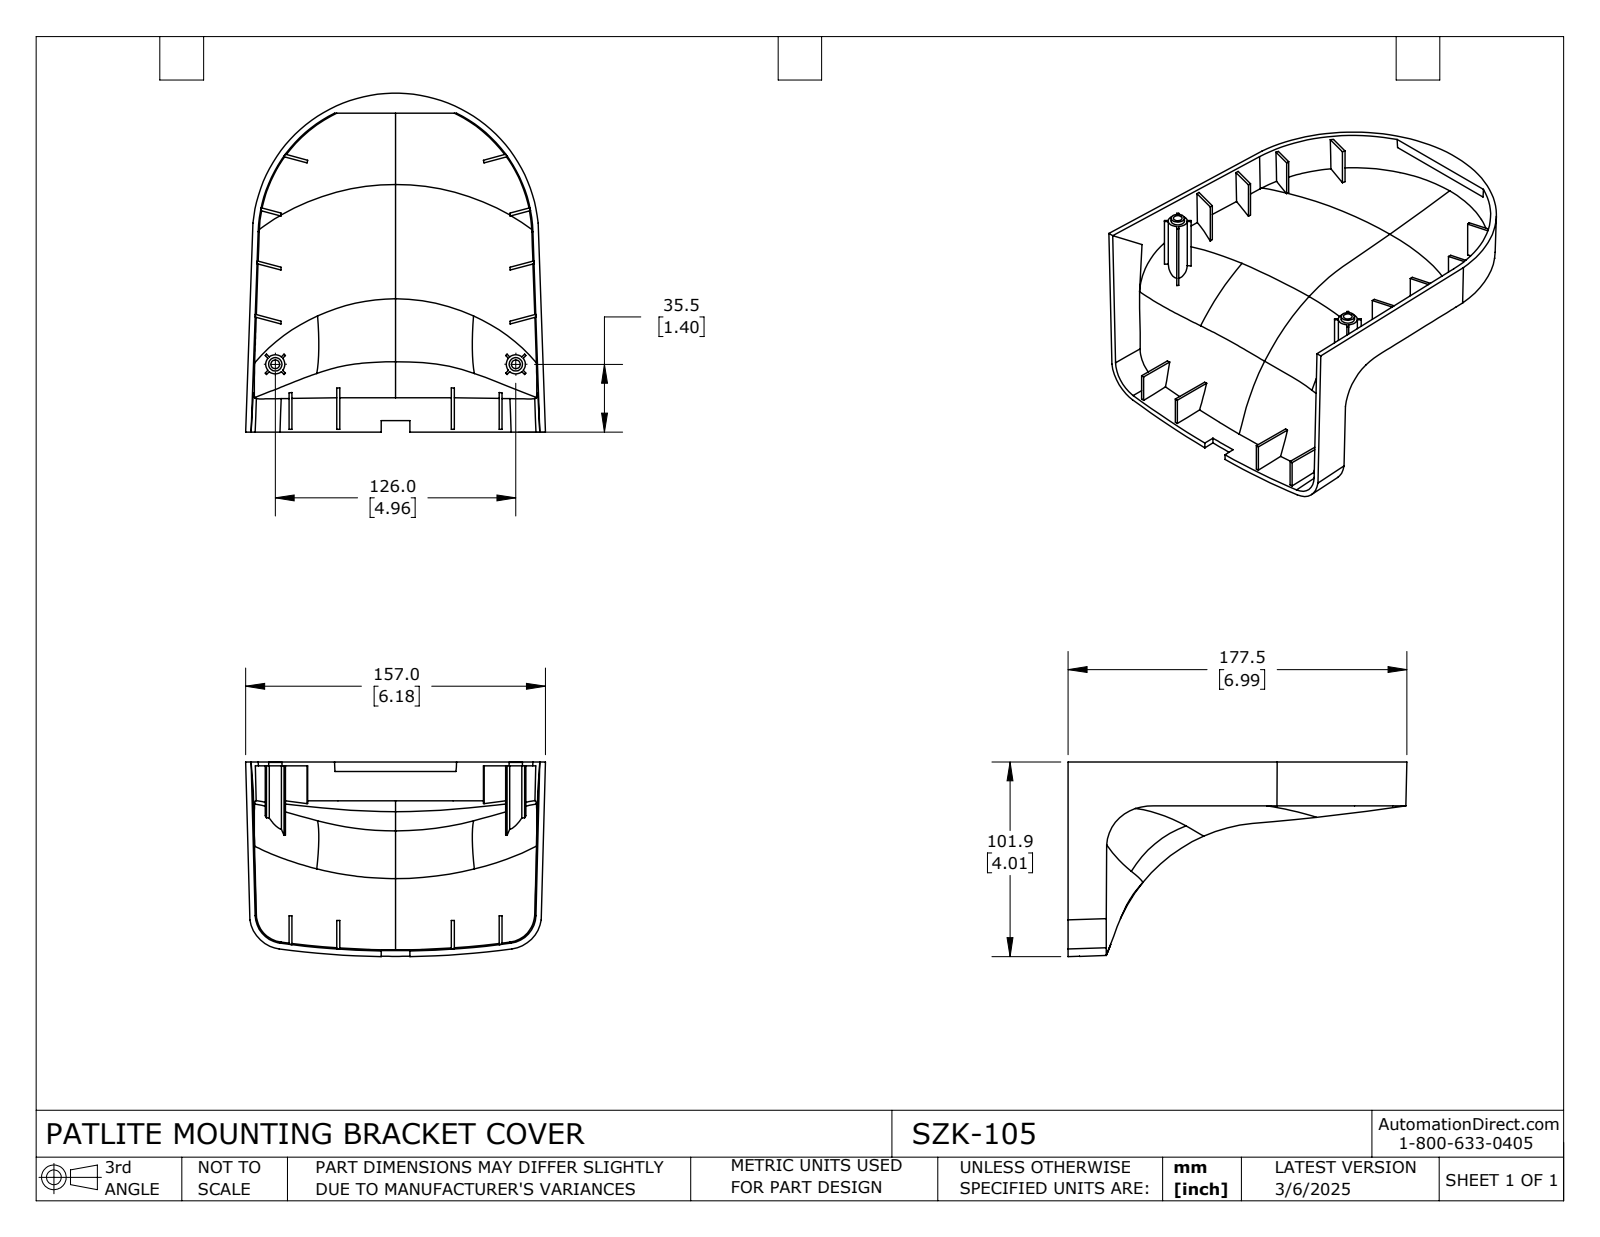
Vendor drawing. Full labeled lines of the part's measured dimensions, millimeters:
Part name (STEP PRODUCT): SZK-105
STEP written by: SolidWorks 2024 (CONFIG_CONTROL_DESIGN)
Units: millimetres
Bodies: 1 solid, 142 faces (90 planar, 18 cylindrical, 34 other)
Overall size (bounding box): 177.5 × 157 × 101.94
Volume: 135 488 mm³ · Surface area: 97 895 mm²
Round holes (diameter × count): ⌀4.58 ×2
Round bosses / shafts (diameter × count): ⌀10 ×2, ⌀7 ×2
Main face-to-face distances: 2.86, 2.87, 1.5, 25, 85, 1.46, 27.3, 30.4, 60, 89.08
Hole centre spacings: 126
